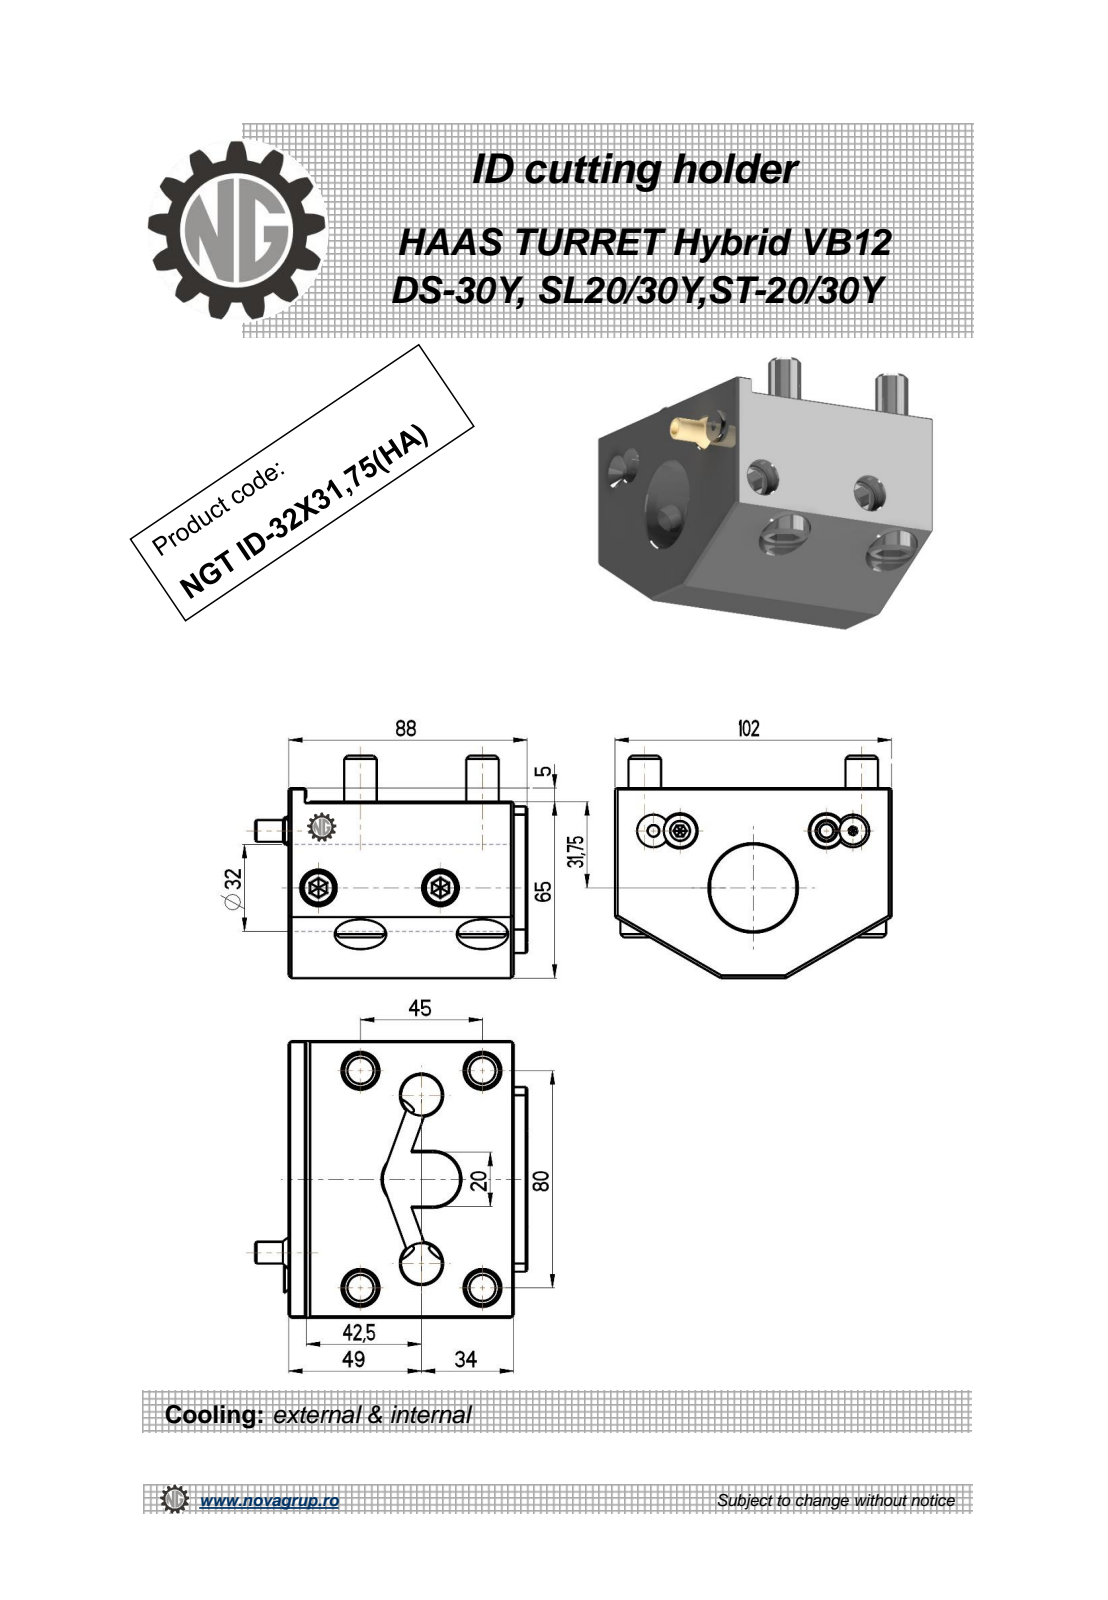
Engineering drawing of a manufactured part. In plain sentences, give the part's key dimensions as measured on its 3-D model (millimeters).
The part is named "NGT_ID_32_31_75_HA". Its 3-D file was written by "PRO/ENGINEER BY PARAMETRIC TECHNOLOGY CORPORATION, 2010280 (CONFIG_CONTROL_DESIGN)". It is 1 solid with 407 faces: 168 planar, 125 cylindrical and 114 other. Overall it measures 102 by 100.34 by 82 millimeters. Its volume is 418 115 cubic millimeters and its surface area 72 888 square millimeters. Round holes: 4 of diameter 13, 4 of diameter 19, 2 of diameter 10.2, 2 of diameter 12.5, 2 of diameter 15, 1 of diameter 5, 1 of diameter 32. Round bosses or shafts: 6 of diameter 12, 4 of diameter 18, 1 of diameter 10, 1 of diameter 8. Partial cylindrical surfaces (rounded edges, fillets, slot ends): 24 of radius 0.61, 20 of radius 0.36, 6 of radius 0.2, 2 of radius 10, 1 of radius 1. The main face-to-face distances are 5, 88, 102, 83, 65, 70, 60, 17, 55, 10. The hole center spacings are 24.23, 74.48, 45, 80, 91.79, 34.21, 62.
